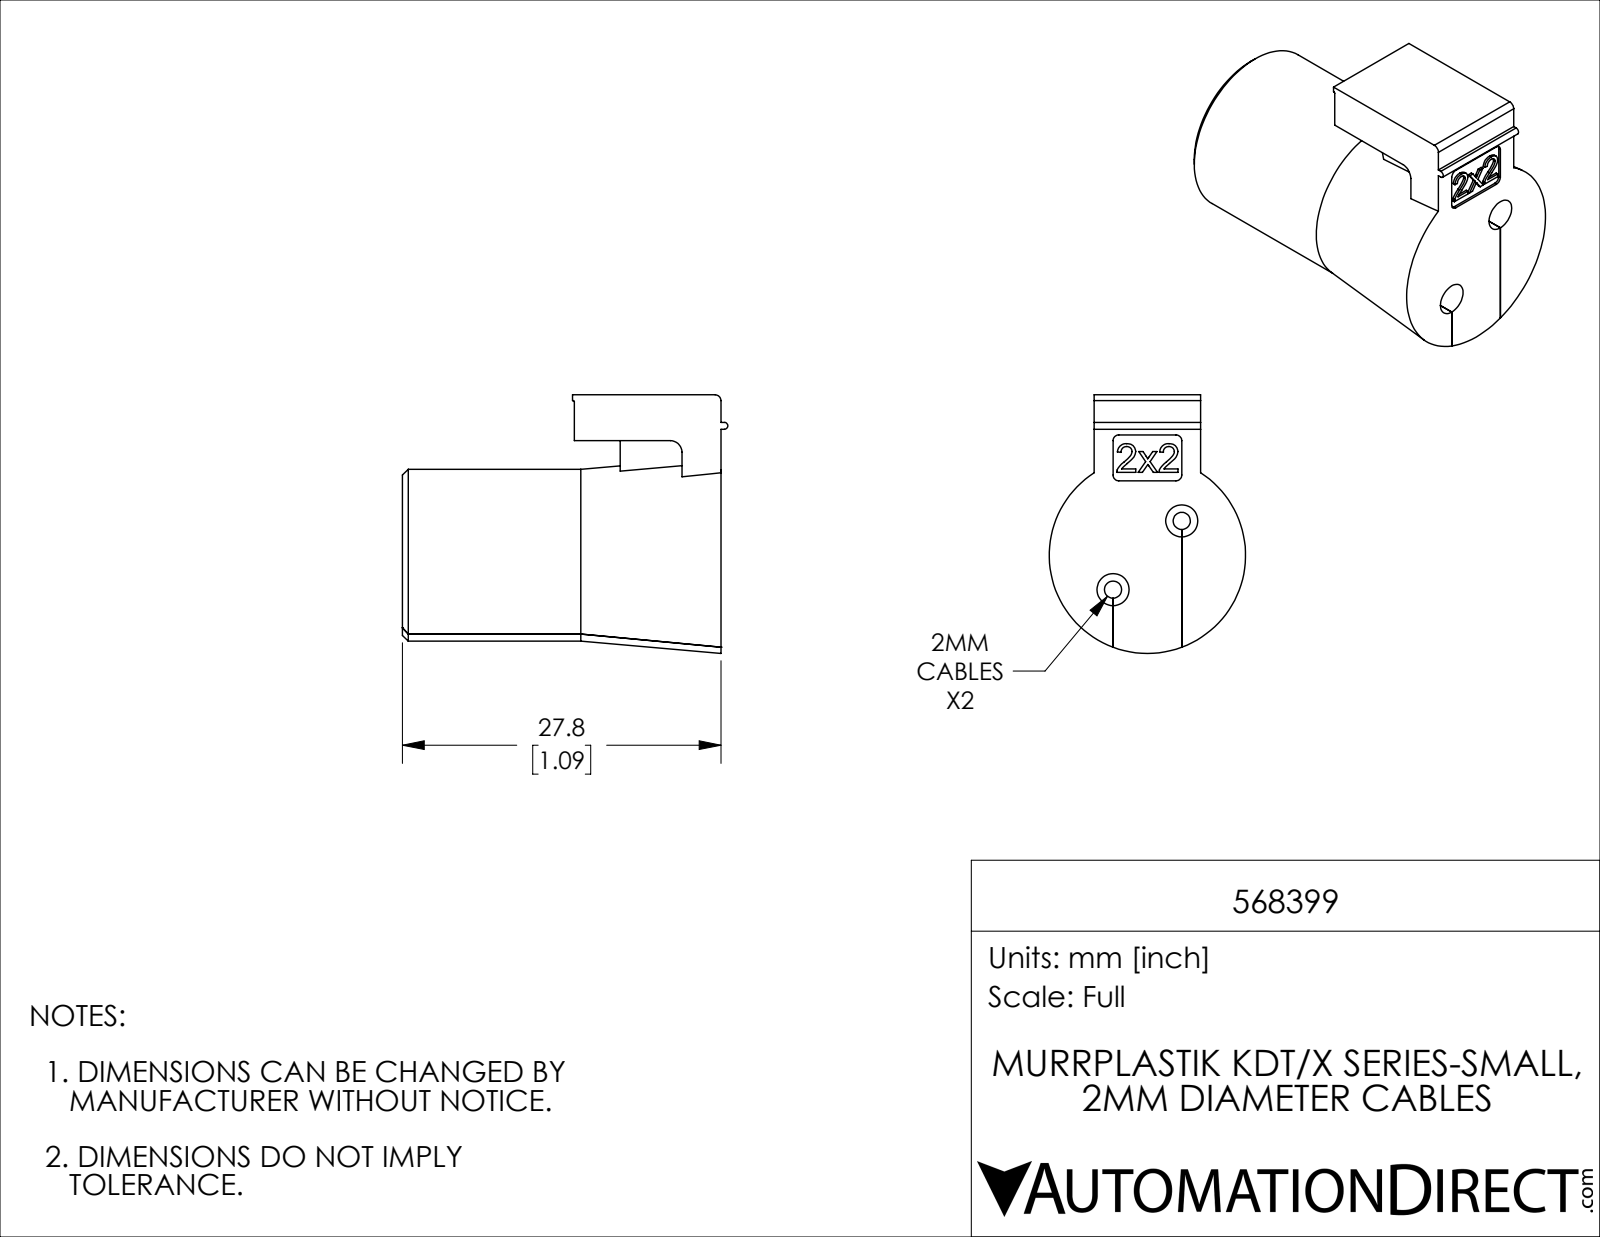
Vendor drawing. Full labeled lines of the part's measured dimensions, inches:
Part name (STEP PRODUCT): 568399
STEP written by: SolidWorks 2019 (CONFIG_CONTROL_DESIGN)
Units: inches
Bodies: 1 solid, 116 faces (50 planar, 28 cylindrical, 38 other)
Overall size (bounding box): 1.118 × 0.889 × 0.675
Volume: 0.335 in³ · Surface area: 5.03 in²
Round holes (diameter × count): ⌀0.059 ×2, ⌀0.11 ×2
Round bosses / shafts (diameter × count): ⌀0.591 ×1
Partial cylindrical surfaces — rounded edges, fillets, slot ends (radius × count): R0.02 ×5, R0.004 ×1, R0.012 ×1, R0.039 ×1
Main face-to-face distances: 0.236, 1.094, 0.065, 0.301, 0.237, 0.236, 0.157, 0.302, 0.065, 0.065
Hole centre spacings: 0.334
